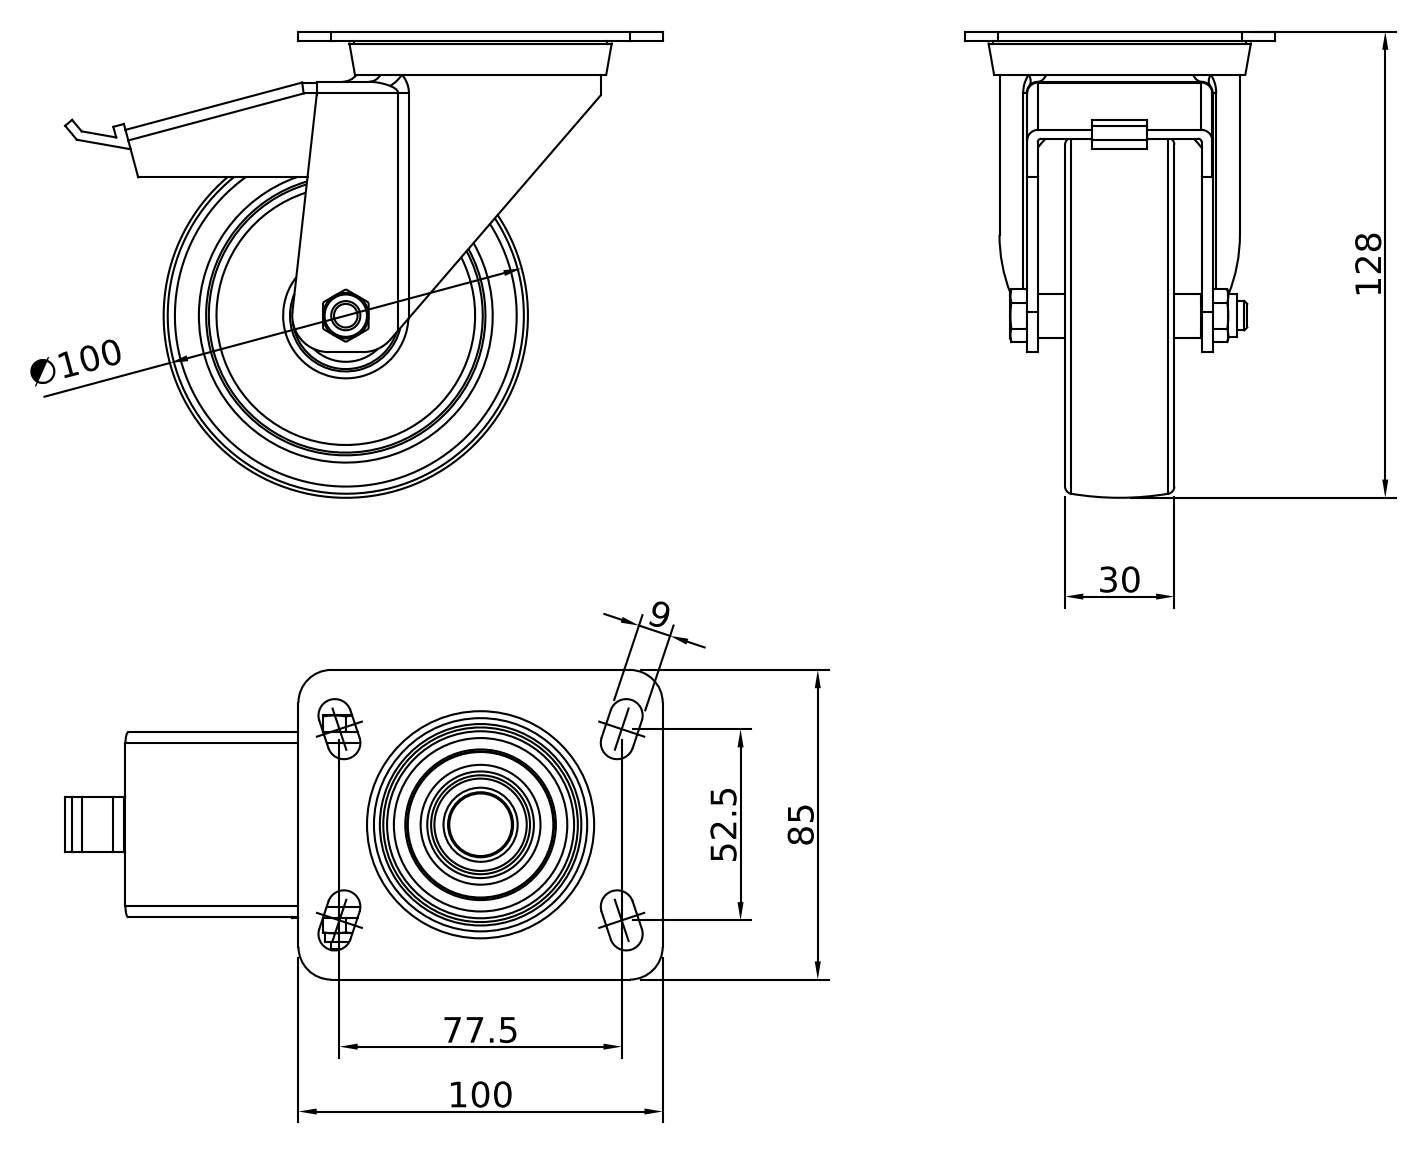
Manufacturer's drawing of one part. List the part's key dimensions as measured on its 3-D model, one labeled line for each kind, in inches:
Part name (STEP PRODUCT): CRUST0000154
STEP written by: Autodesk Inventor 2022 (AUTOMOTIVE_DESIGN)
Units: inches
Bodies: 1 solid, 174 faces (80 planar, 40 cylindrical, 54 other)
Overall size (bounding box): 6.459 × 5.039 × 3.346
Volume: 14.31 in³ · Surface area: 126 in²
Round holes (diameter × count): ⌀0.354 ×1, ⌀1.589 ×1, ⌀2.402 ×1
Round bosses / shafts (diameter × count): ⌀2.74 ×1, ⌀0.472 ×1, ⌀0.458 ×1, ⌀0.315 ×1
Partial cylindrical surfaces — rounded edges, fillets, slot ends (radius × count): R0.177 ×8, R0.118 ×6, R0.039 ×4, R0.354 ×4, R0.197 ×2, R0.394 ×2, R1.299 ×1
Main face-to-face distances: 0.098, 0.295, 1.476, 0.413, 1.89, 0.118, 1.594, 0.551, 0.453, 1.772
